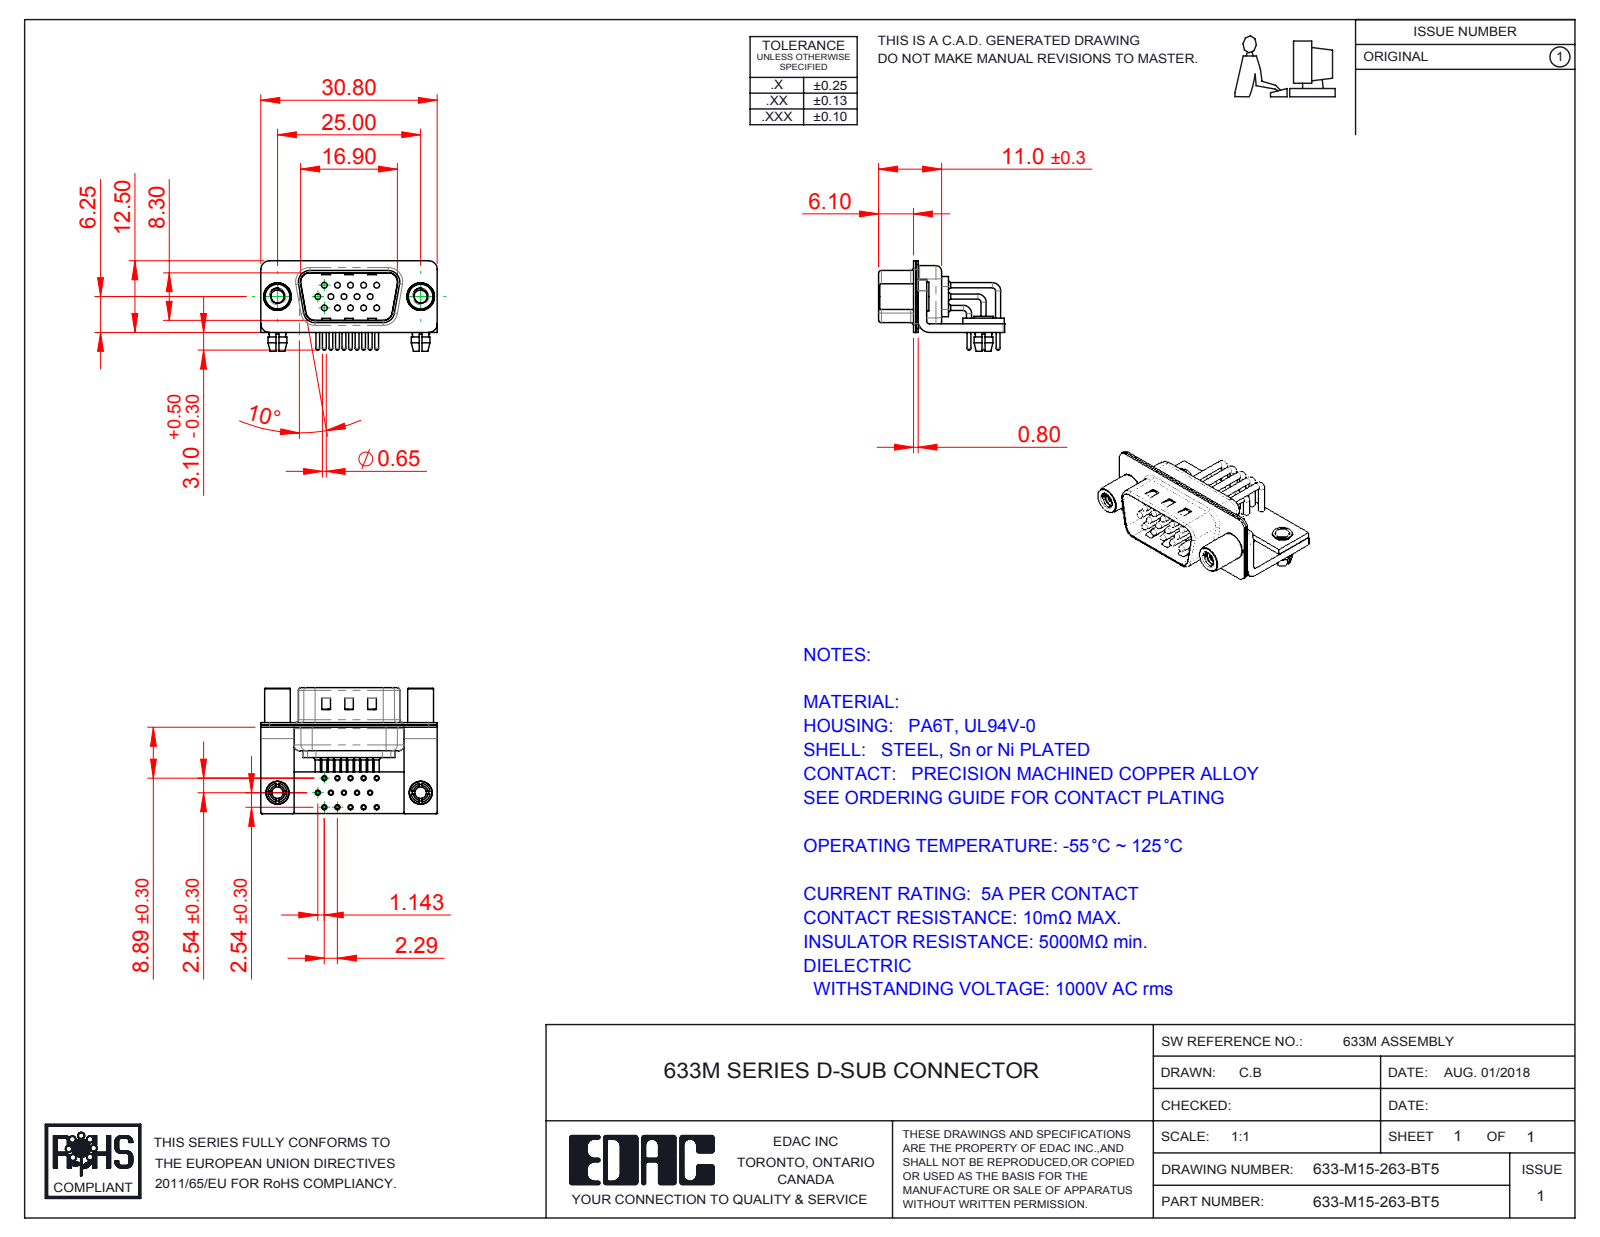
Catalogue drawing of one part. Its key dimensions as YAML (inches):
part_name: "633M Shell Rear_15 Contacts; 633M Shell Front_15 Contacts; 633M Housing_15 Contacts; 633-M15-263-BT5 (+7 more)"
step_written_by: "SolidWorks 2016 (CONFIG_CONTROL_DESIGN)"
units: inches
bodies: {solids: 25, faces: 2176, planar: 1143, cylindrical: 795, other: 238}
overall_size: [1.213, 0.866, 0.622]
volume: 0.128
surface_area: 9.821
round_holes:
  - {diameter: 0.079, count: 17}
  - {diameter: 0.035, count: 15}
  - {diameter: 0.039, count: 15}
  - {diameter: 0.067, count: 15}
  - {diameter: 0.089, count: 2}
  - {diameter: 0.098, count: 2}
  - {diameter: 0.126, count: 2}
  - {diameter: 0.157, count: 2}
  - {diameter: 0.189, count: 2}
round_bosses_or_shafts:
  - {diameter: 0.035, count: 16}
  - {diameter: 0.059, count: 15}
  - {diameter: 0.026, count: 15}
  - {diameter: 0.197, count: 2}
  - {diameter: 0.193, count: 2}
  - {diameter: 0.177, count: 2}
  - {diameter: 0.157, count: 2}
  - {diameter: 0.134, count: 2}
partial_cylinders:
  - {radius: 0.01, count: 16}
  - {radius: 0.059, count: 16}
  - {radius: 0.04, count: 15}
  - {radius: 0.079, count: 13}
  - {radius: 0.02, count: 9}
  - {radius: 0.063, count: 8}
  - {radius: 0.024, count: 4}
  - {radius: 0.026, count: 4}
face_to_face_distances: [0.016, 0.059, 0.031, 0.039, 0.033, 0.075, 0.098, 0.049, 0.409, 0.376]
hole_center_spacings: [0.09, 0.18, 0.09, 0.156, 0.109, 0.168, 0.238, 0.27]
